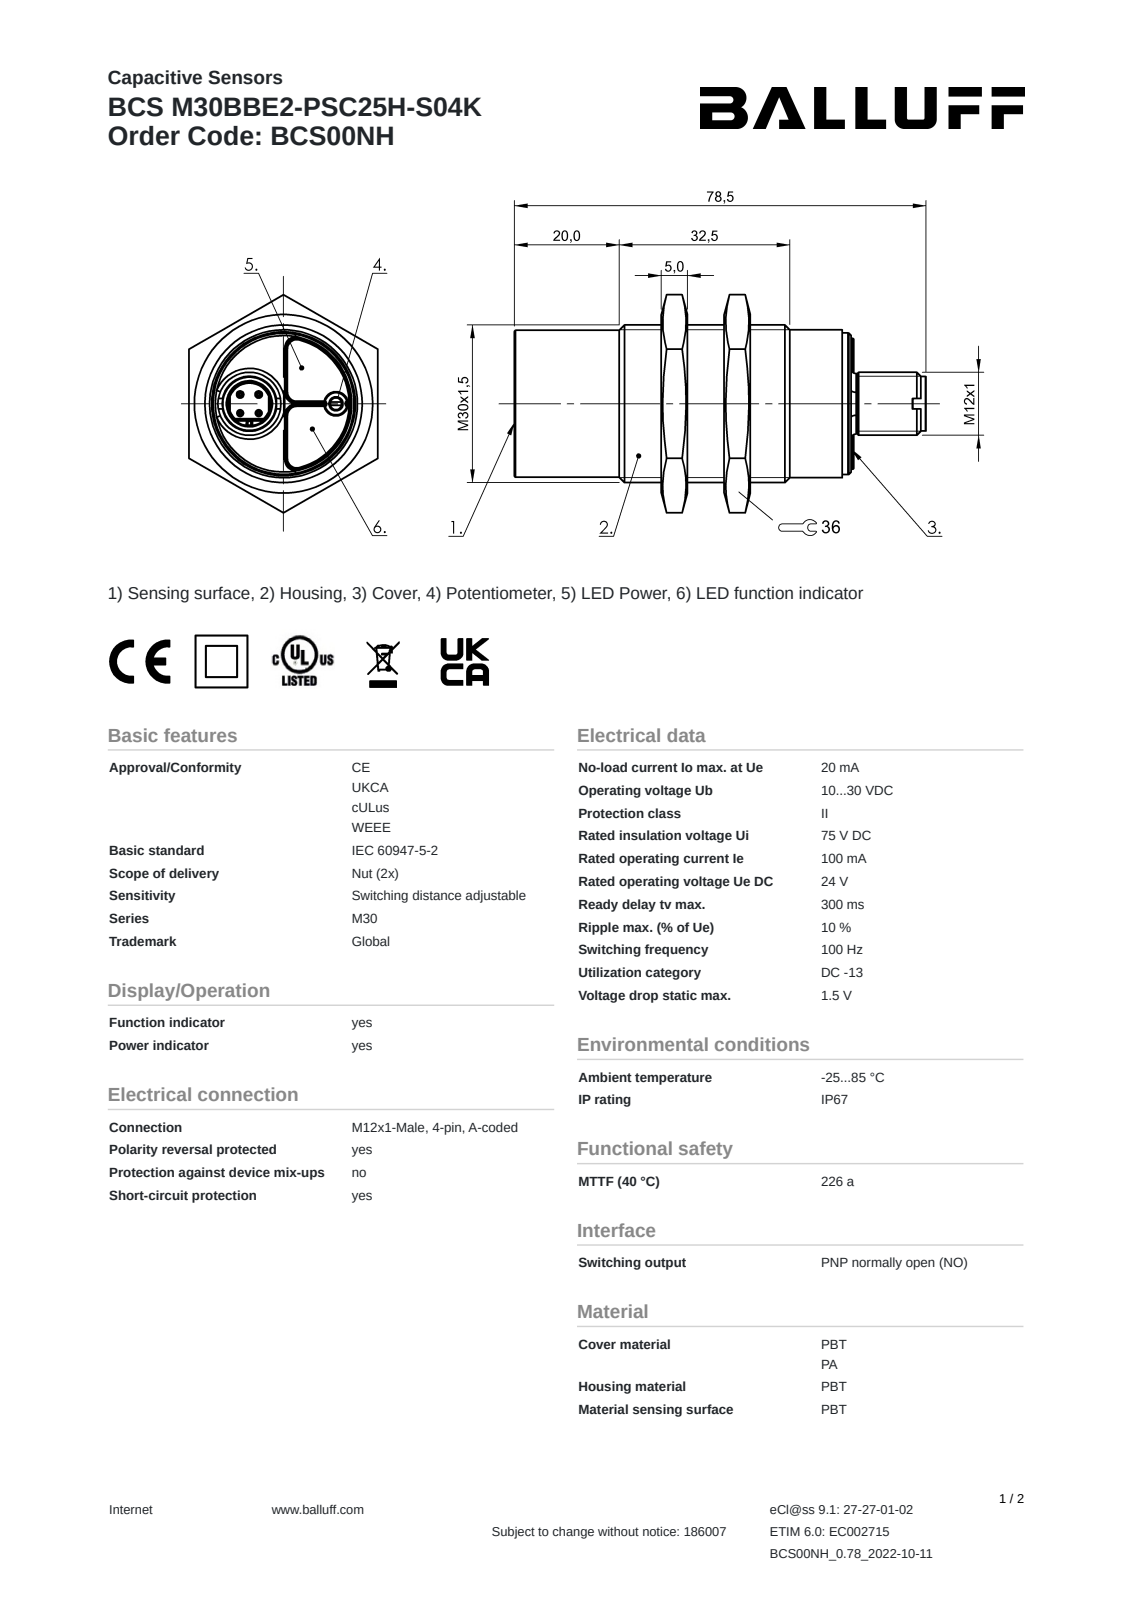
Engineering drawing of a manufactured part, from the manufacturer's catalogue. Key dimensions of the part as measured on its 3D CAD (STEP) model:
Part name (STEP PRODUCT): BCS00NH
STEP written by: SolidWorks 2021 (AUTOMOTIVE_DESIGN)
Units: inches
Bodies: 3 solids, 184 faces (73 planar, 52 cylindrical, 59 other)
Overall size (bounding box): 3.091 × 1.637 × 1.417
Volume: 2.933 in³ · Surface area: 18.61 in²
Round holes (diameter × count): ⌀0.106 ×1, ⌀0.331 ×1, ⌀1.117 ×1
Round bosses / shafts (diameter × count): ⌀0.039 ×4, ⌀1.181 ×1, ⌀1.11 ×1, ⌀1.102 ×1, ⌀1.063 ×1, ⌀0.472 ×1, ⌀0.453 ×1, ⌀0.407 ×1
Partial cylindrical surfaces — rounded edges, fillets, slot ends (radius × count): R0.004 ×8, R0.01 ×5, R0.006 ×2, R0.024 ×1, R0.041 ×1, R0.156 ×1, R0.164 ×1, R0.182 ×1
Main face-to-face distances: 0.433, 0.197, 1.417, 0.236, 1.575, 1.142, 0.63, 1.772, 1.339, 0.756
Hole centre spacings: 0.256, 0.38, 0.636
